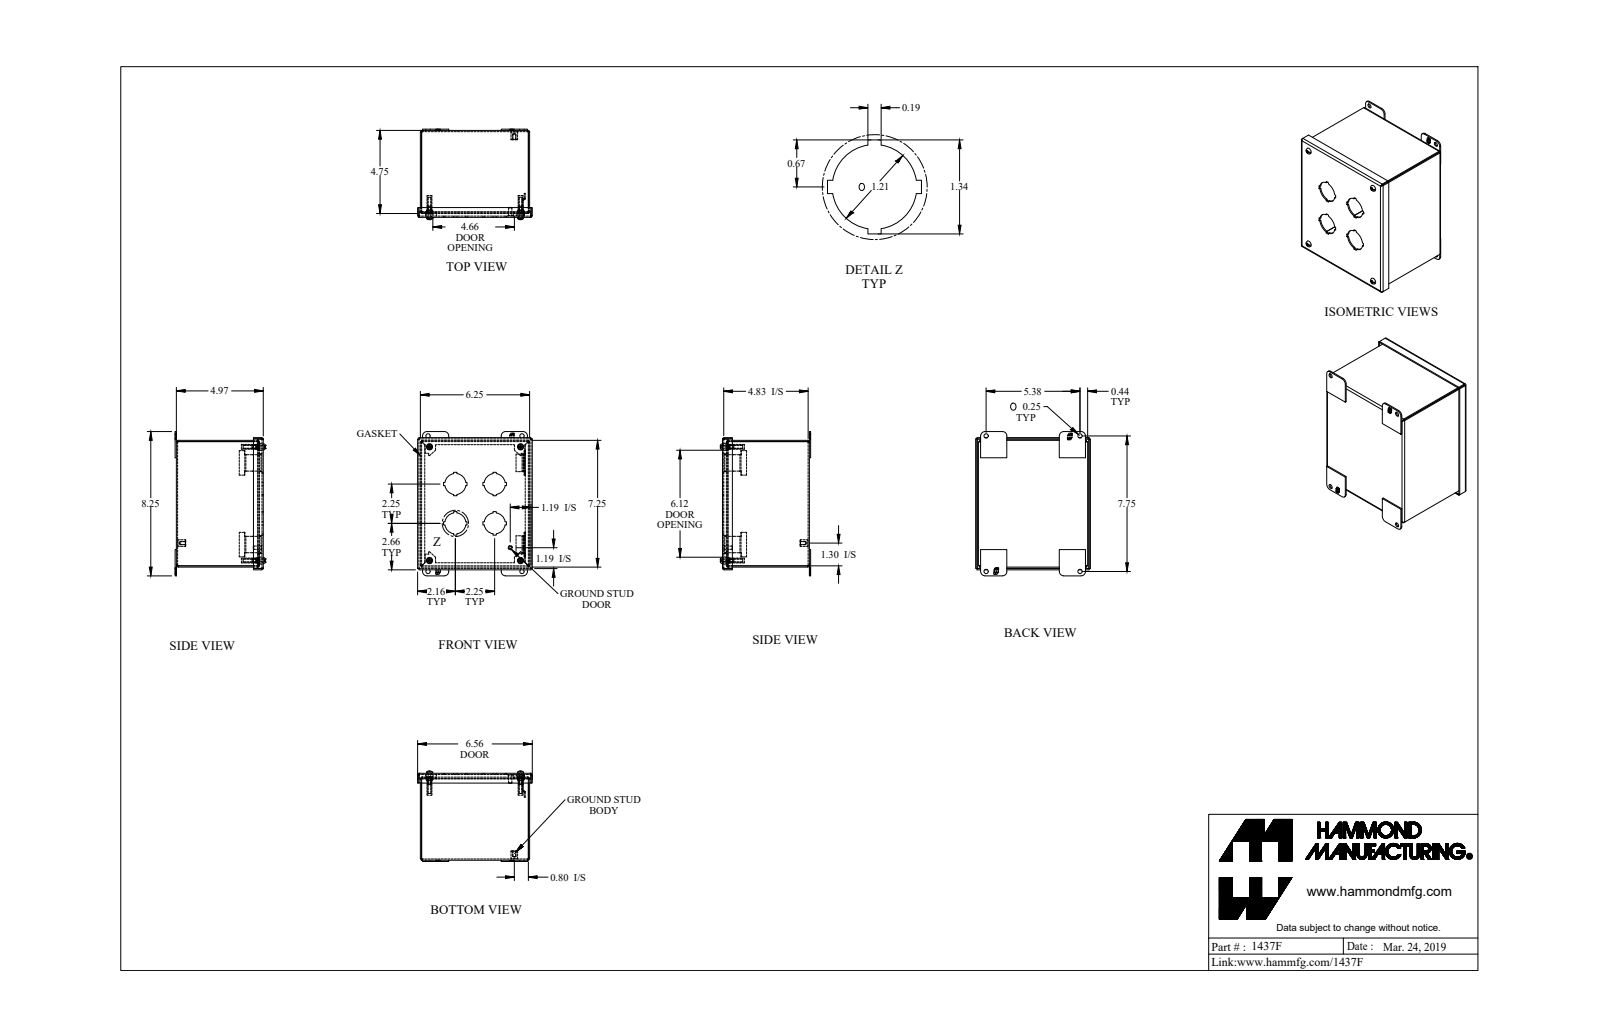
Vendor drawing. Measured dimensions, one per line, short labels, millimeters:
name: 1437F_Default
written by: SolidWorks 2019 (CONFIG_CONTROL_DESIGN)
unit: mm
bodies: 23 solids, 779 faces (547 planar, 176 cylindrical, 56 other)
size: 209.6 × 166.7 × 131.3
volume: 332 700 mm³; area: 350 300 mm²
holes: 8× ⌀6.4, 4× ⌀4, 4× ⌀10.3, 4× ⌀30.7, 1× ⌀4
bosses: 4× ⌀9.9, 4× ⌀7, 4× ⌀4.8, 4× ⌀3.8, 1× ⌀9.5, 1× ⌀6.4, 1× ⌀4.8
rounds: 12× R0.9, 12× R2.7, 8× R6.4, 4× R0.7, 4× R2.2, 4× R4.1, 4× R4.3
face distances: 1.8, 124.5, 156.9, 182.3, 126.3, 122.6, 158.8, 155.1, 184.2, 180.5
hole spacings: 165.1, 181, 117.3, 16, 57.2, 65.8, 132.3, 132.4
